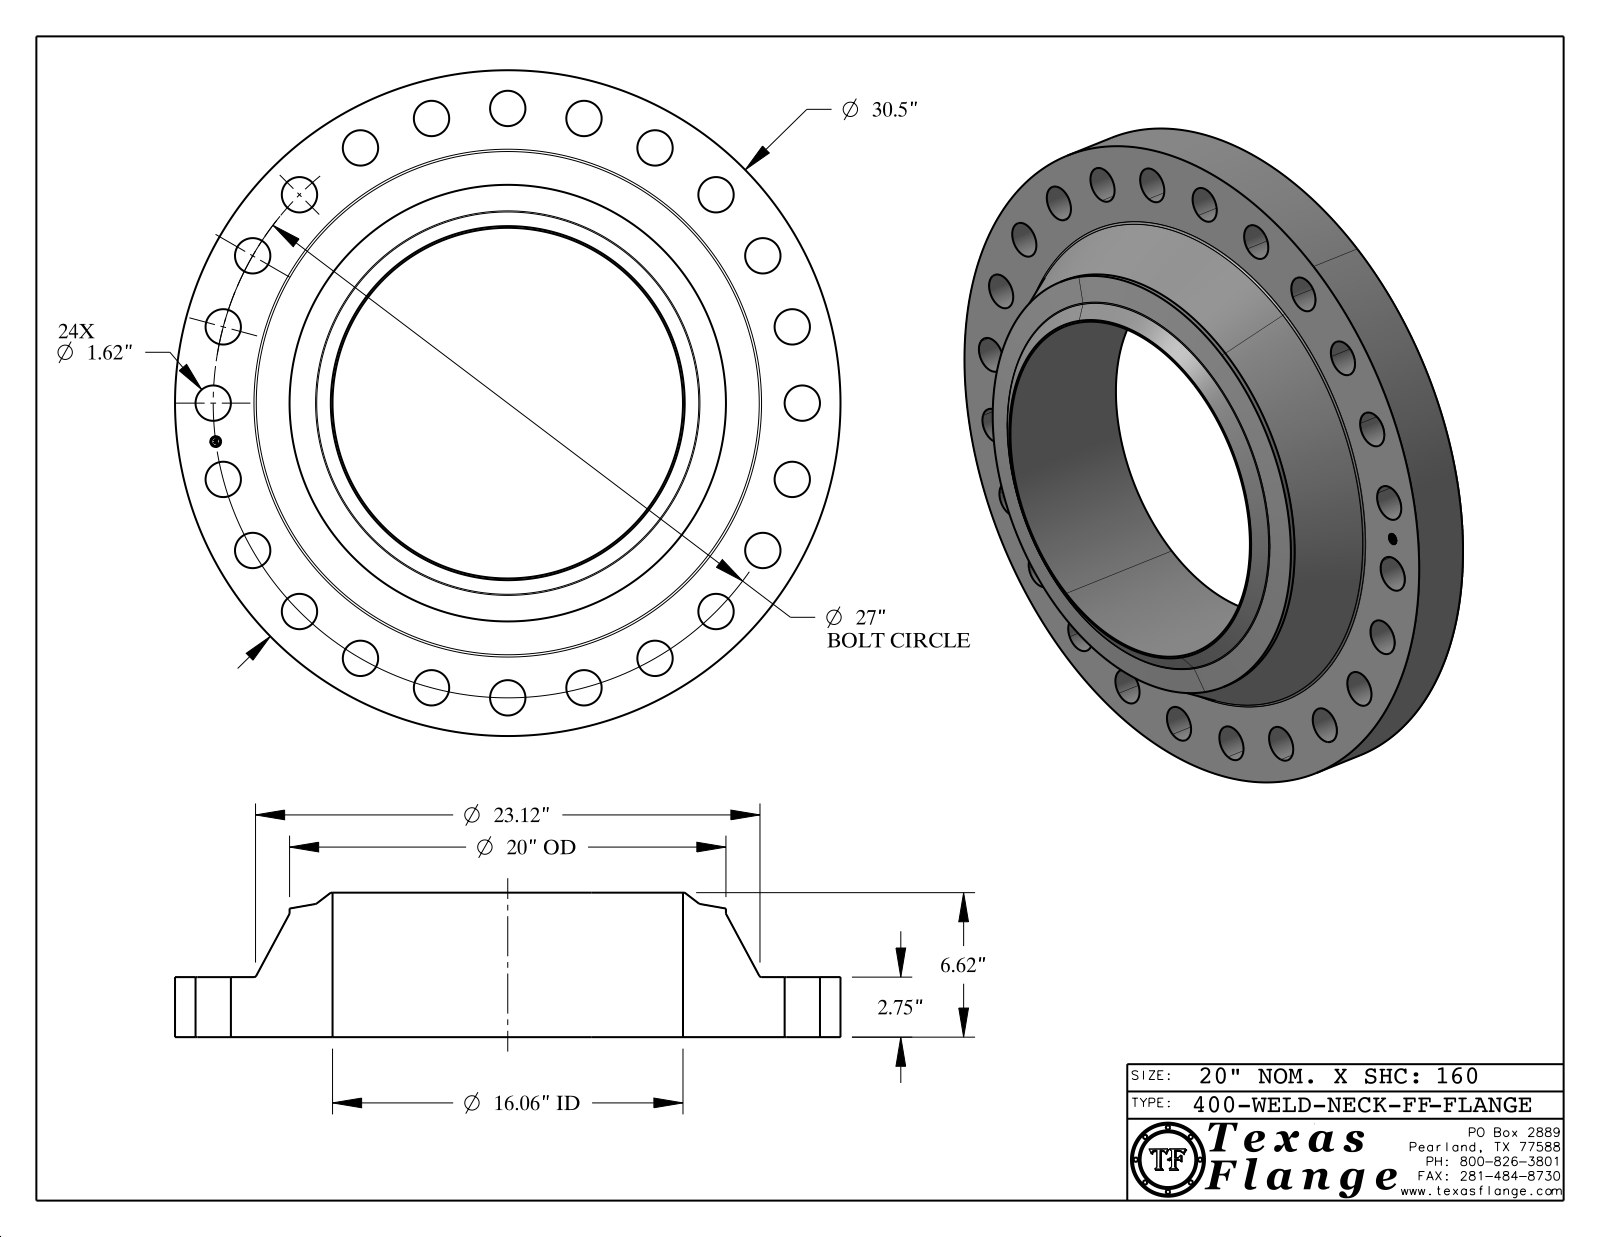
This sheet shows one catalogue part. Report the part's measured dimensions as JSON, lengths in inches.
{"part_name": "400-WELD-NECK-FF", "step_written_by": "CATIA V5 STEP AP214 (AUTOMOTIVE_DESIGN)", "units": "inches", "bodies": {"solids": 1, "faces": 452, "planar": 368, "cylindrical": 74, "other": 10}, "overall_size": [30.5, 30.5, 6.62], "volume_in3": 1843, "surface_area_in2": 2032, "round_holes": [[1.62, 24], [0.495, 1], [16.062, 1]], "round_bosses_or_shafts": [[0.03, 8], [30.5, 1], [20, 1], [0.39, 1]], "face_to_face_distances": [2.75, 6.62, 3.87, 2.735, 0.015, 3.885, 0.148, 0.144, 0.027, 0.096], "hole_center_spacings": [13.5, 3.524, 6.988, 10.333, 16.437, 24.945, 26.769, 21.421]}
